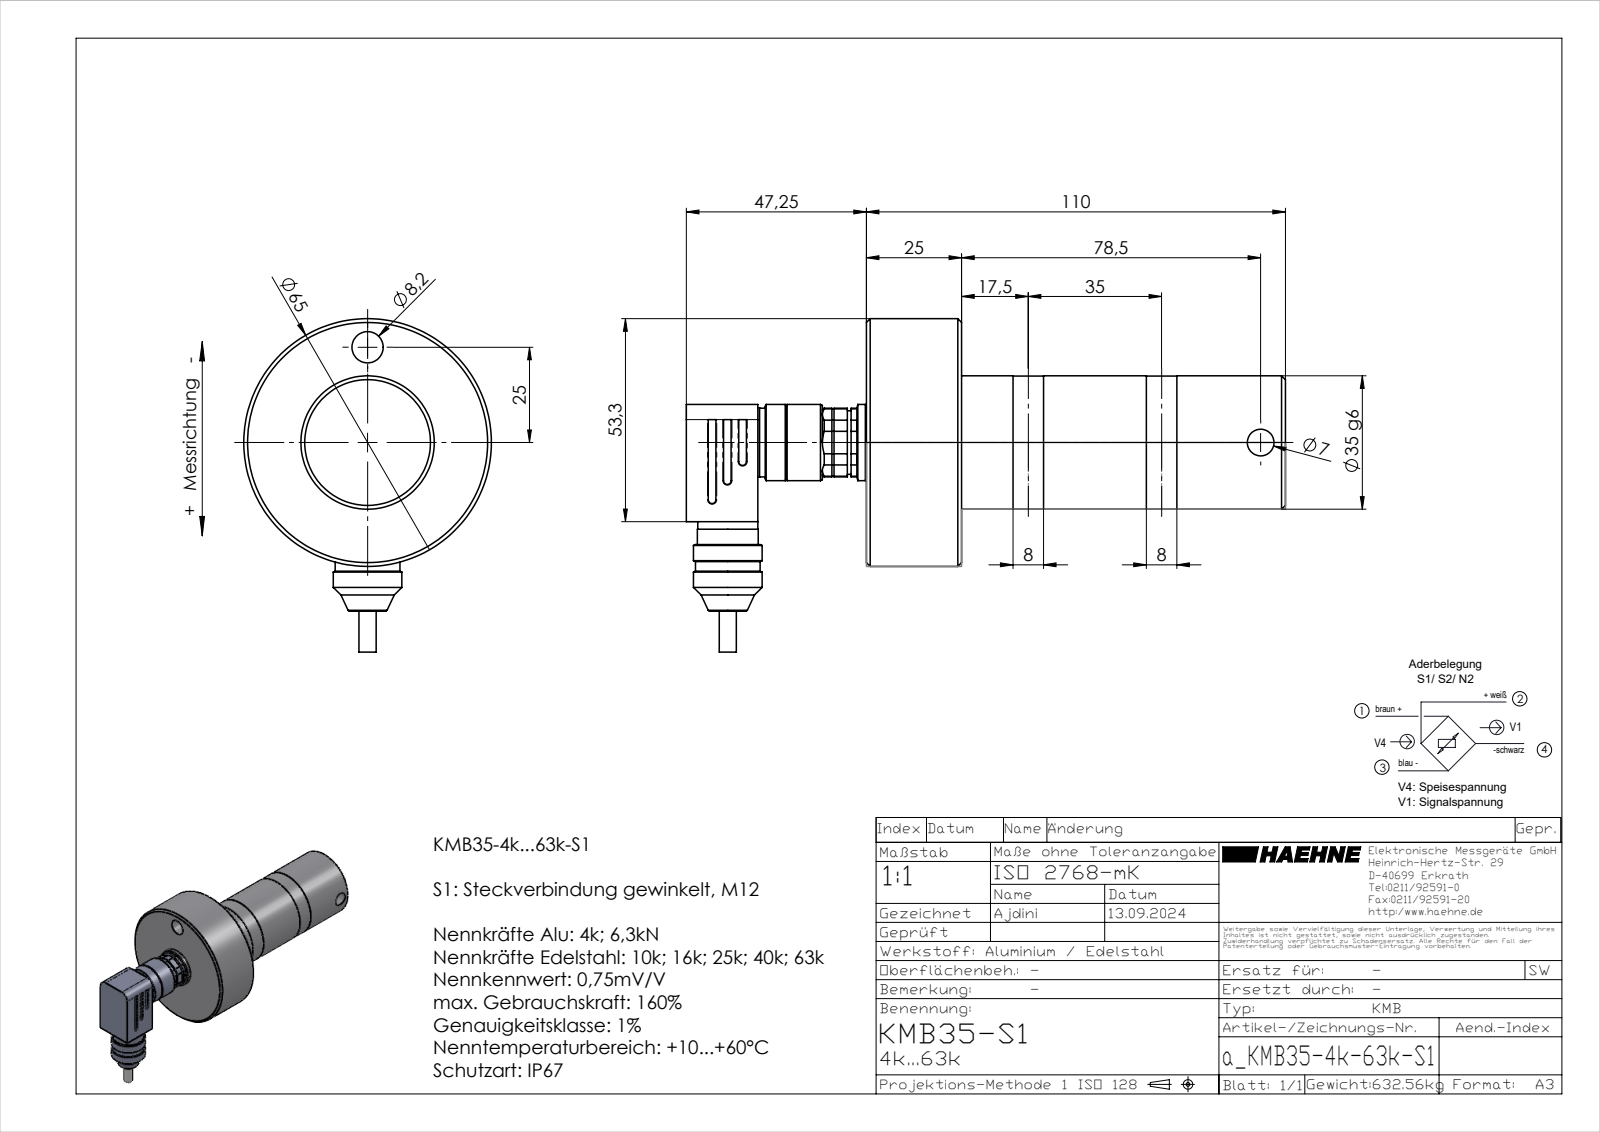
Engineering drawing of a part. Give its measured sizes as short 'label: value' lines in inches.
name: S1; a_KMB35-4k-63k-S1
written by: SolidWorks 2023 (CONFIG_CONTROL_DESIGN)
unit: in
bodies: 2 solids, 208 faces (92 planar, 79 cylindrical, 37 other)
size: 6.191 × 3.444 × 2.559
volume: 9.533 in³; area: 50.53 in²
holes: 5× ⌀0.026, 1× ⌀0.276, 1× ⌀0.323, 1× ⌀0.4, 1× ⌀0.551, 1× ⌀0.62, 1× ⌀0.63, 1× ⌀0.669, 1× ⌀0.709
bosses: 4× ⌀0.059, 1× ⌀2.559, 1× ⌀1.378, 1× ⌀1.374, 1× ⌀0.787, 1× ⌀0.717, 1× ⌀0.709, 1× ⌀0.657
rounds: 12× R0.008, 3× R0.039, 2× R0.157
face distances: 0.984, 3.346, 4.331, 6.191, 2.844, 1.86, 0.787, 1.122, 5.453, 2.106
hole spacings: 0.045, 0.028, 0.028, 0.276, 0.304, 0.682, 0.708, 0.319
